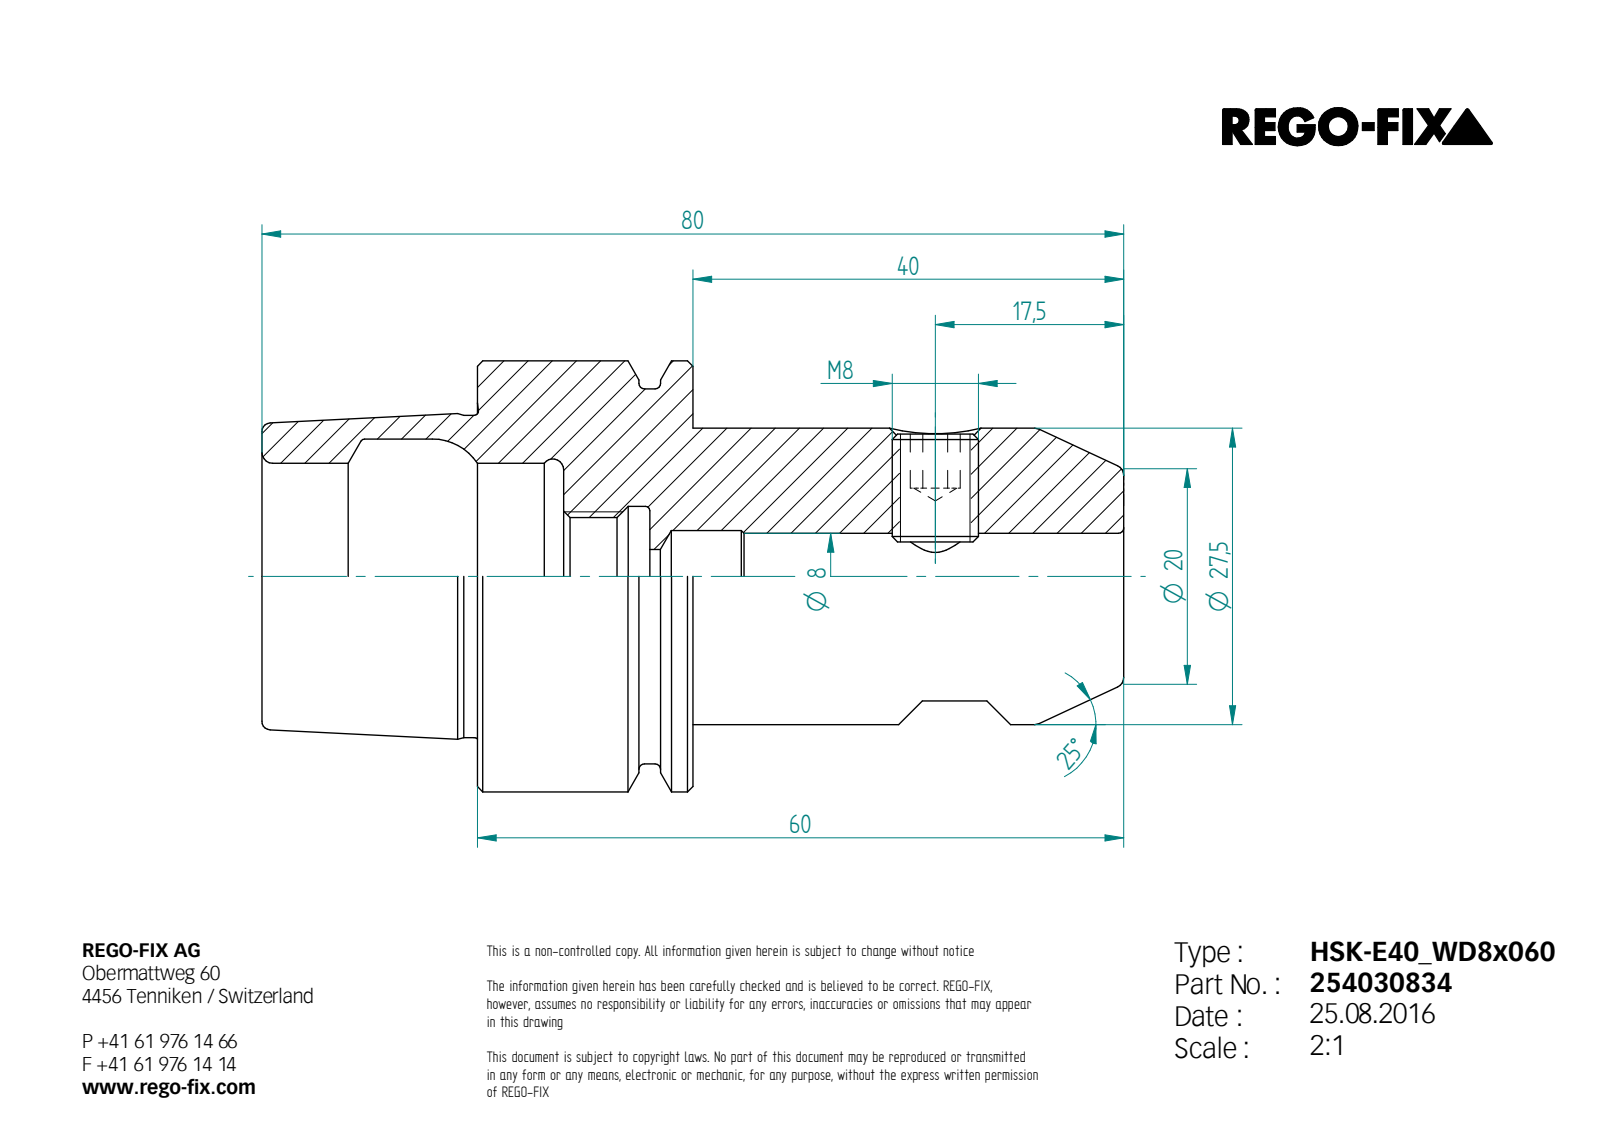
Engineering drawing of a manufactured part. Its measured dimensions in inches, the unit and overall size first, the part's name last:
Units: inches
Overall size (bounding box): 3.15 × 1.575 × 1.575
Round holes (diameter × count): ⌀0.197 ×1, ⌀0.262 ×1, ⌀0.315 ×1, ⌀0.335 ×1, ⌀0.43 ×1, ⌀0.512 ×1, ⌀0.827 ×1, ⌀1.004 ×1
Round bosses / shafts (diameter × count): ⌀1.575 ×1, ⌀1.37 ×1, ⌀1.178 ×1, ⌀1.083 ×1, ⌀0.315 ×1
Main face-to-face distances: 0.787, 1.575, 0.315, 2.362, 0.472, 2.047, 1.102, 3.15, 0.157, 1.417
Volume: 2.797 in³ · Surface area: 22.05 in²
Bodies: 2 solids, 69 faces (25 planar, 15 cylindrical, 29 other)
STEP written by: Unknown (AUTOMOTIVE_DESIGN)
